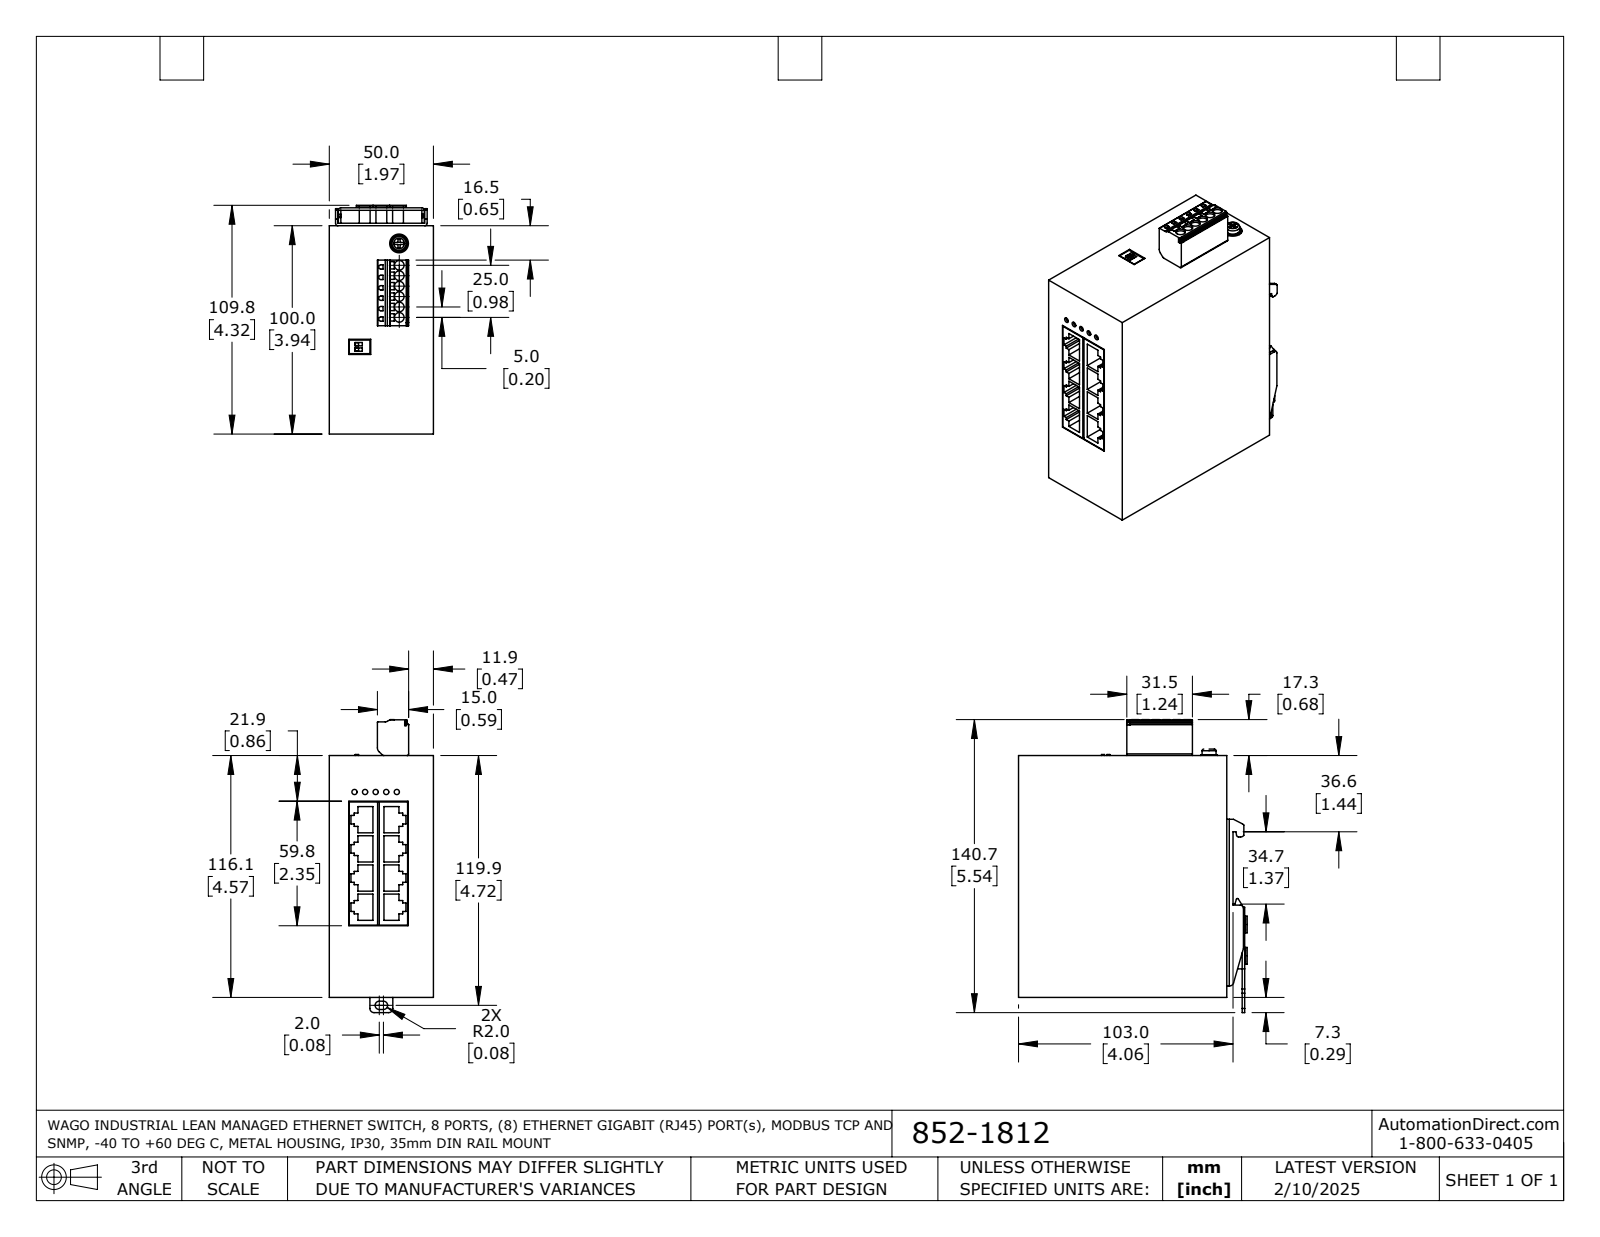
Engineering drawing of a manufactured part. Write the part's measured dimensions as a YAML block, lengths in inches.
part_name: "852-1812"
step_written_by: "SolidWorks 2021 (AUTOMOTIVE_DESIGN)"
units: inches
bodies: {solids: 1, faces: 455, planar: 329, cylindrical: 119, other: 7}
overall_size: [5.537, 4.323, 1.969]
volume: 35.72
surface_area: 92.28
round_holes:
  - {diameter: 0.181, count: 6}
  - {diameter: 0.098, count: 5}
  - {diameter: 0.394, count: 2}
  - {diameter: 0.354, count: 1}
round_bosses_or_shafts:
  - {diameter: 0.315, count: 4}
  - {diameter: 0.205, count: 3}
  - {diameter: 0.264, count: 1}
partial_cylinders:
  - {radius: 0.004, count: 14}
  - {radius: 0.079, count: 10}
  - {radius: 0.041, count: 6}
  - {radius: 0.104, count: 6}
  - {radius: 0.047, count: 5}
  - {radius: 0.02, count: 4}
  - {radius: 0.008, count: 3}
  - {radius: 0.031, count: 1}
face_to_face_distances: [1.969, 0.047, 4.571, 3.984, 0.291, 3.937, 0.339, 0.244, 4.228, 4.276]
hole_center_spacings: [0.197, 0.2, 0.394, 0.4, 0.591, 0.6, 0.787, 3.473]
